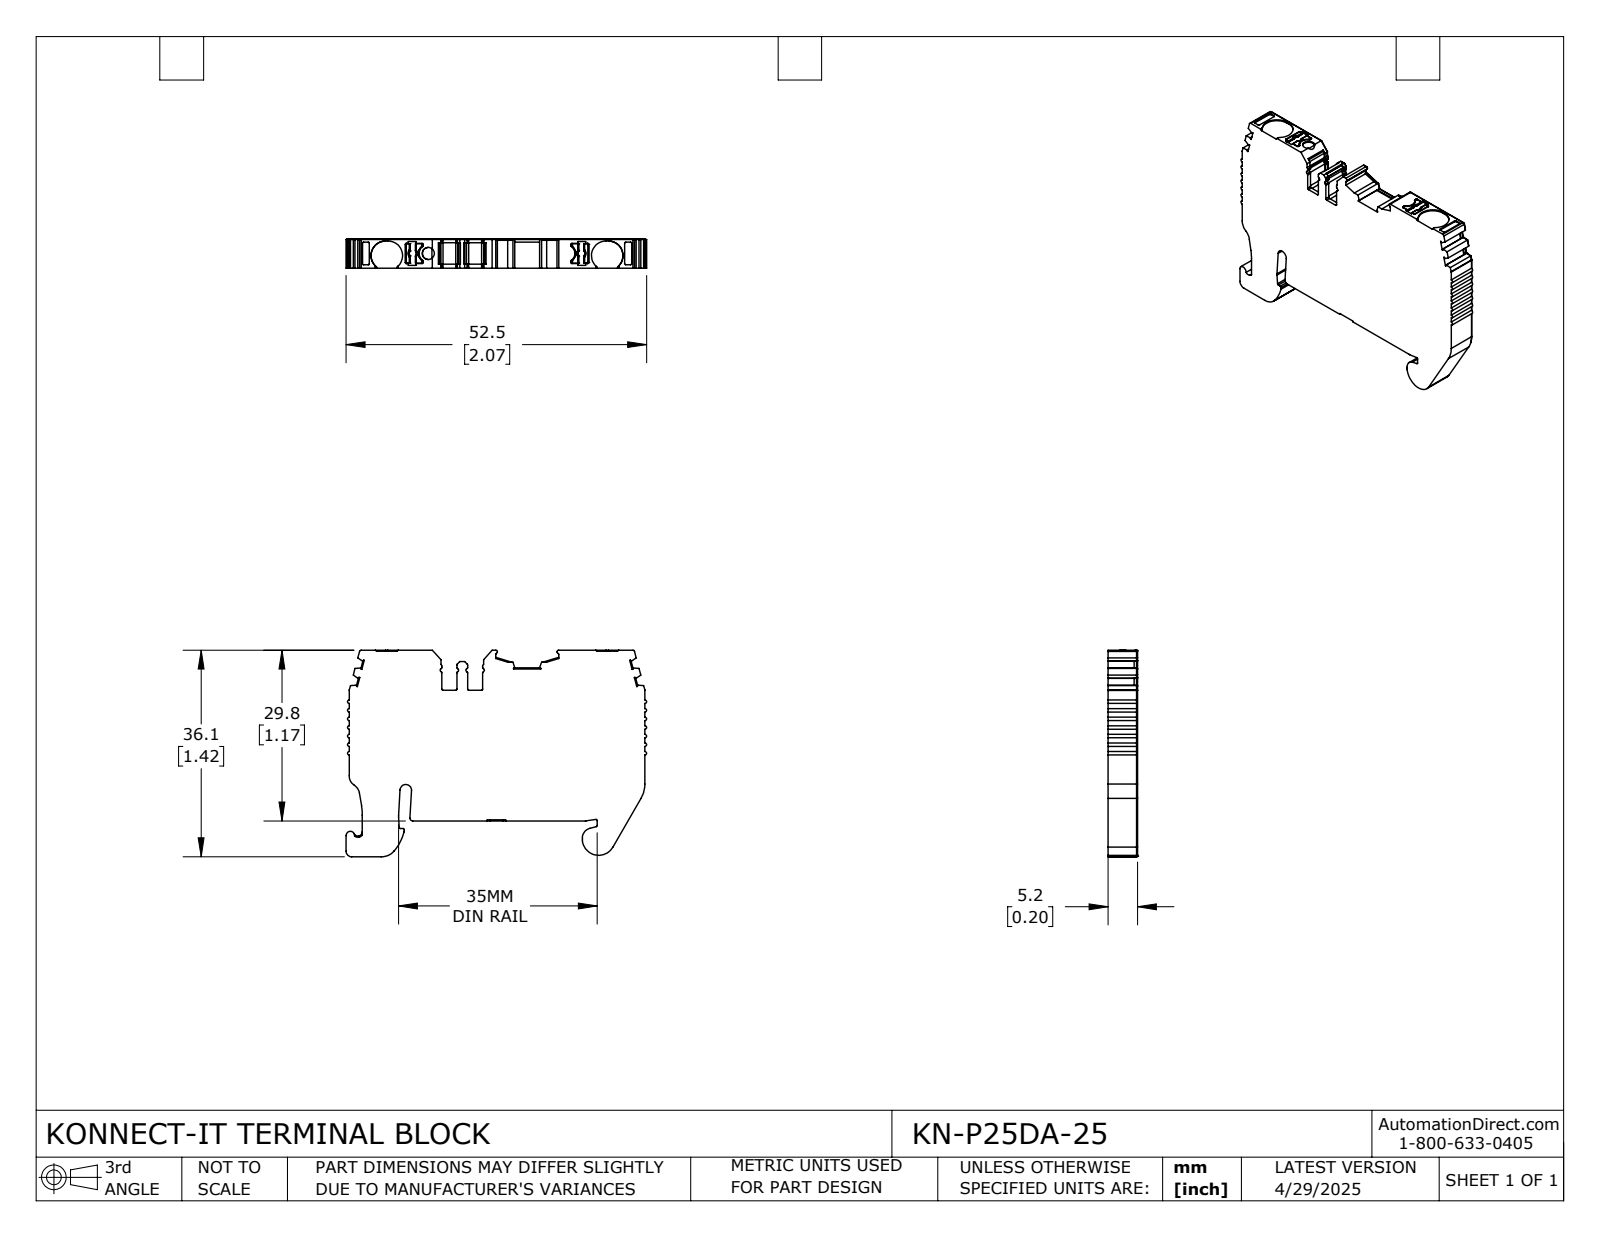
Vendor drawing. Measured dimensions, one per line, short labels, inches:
name: KN-P25DA-25
written by: SolidWorks 2024 (CONFIG_CONTROL_DESIGN)
unit: in
bodies: 1 solid, 584 faces (308 planar, 239 cylindrical, 37 other)
size: 2.066 × 1.42 × 0.203
volume: 0.468 in³; area: 6.63 in²
holes: 1× ⌀0.083
rounds: 54× R0.008, 39× R0.012, 18× R0.02, 17× R0.004, 9× R0.016, 8× R0.006, 4× R0.1, 3× R0.039
face distances: 0.203, 1.166, 1.174, 2.033, 0.177, 0.197, 0.246, 1.412, 0.079, 1.42
